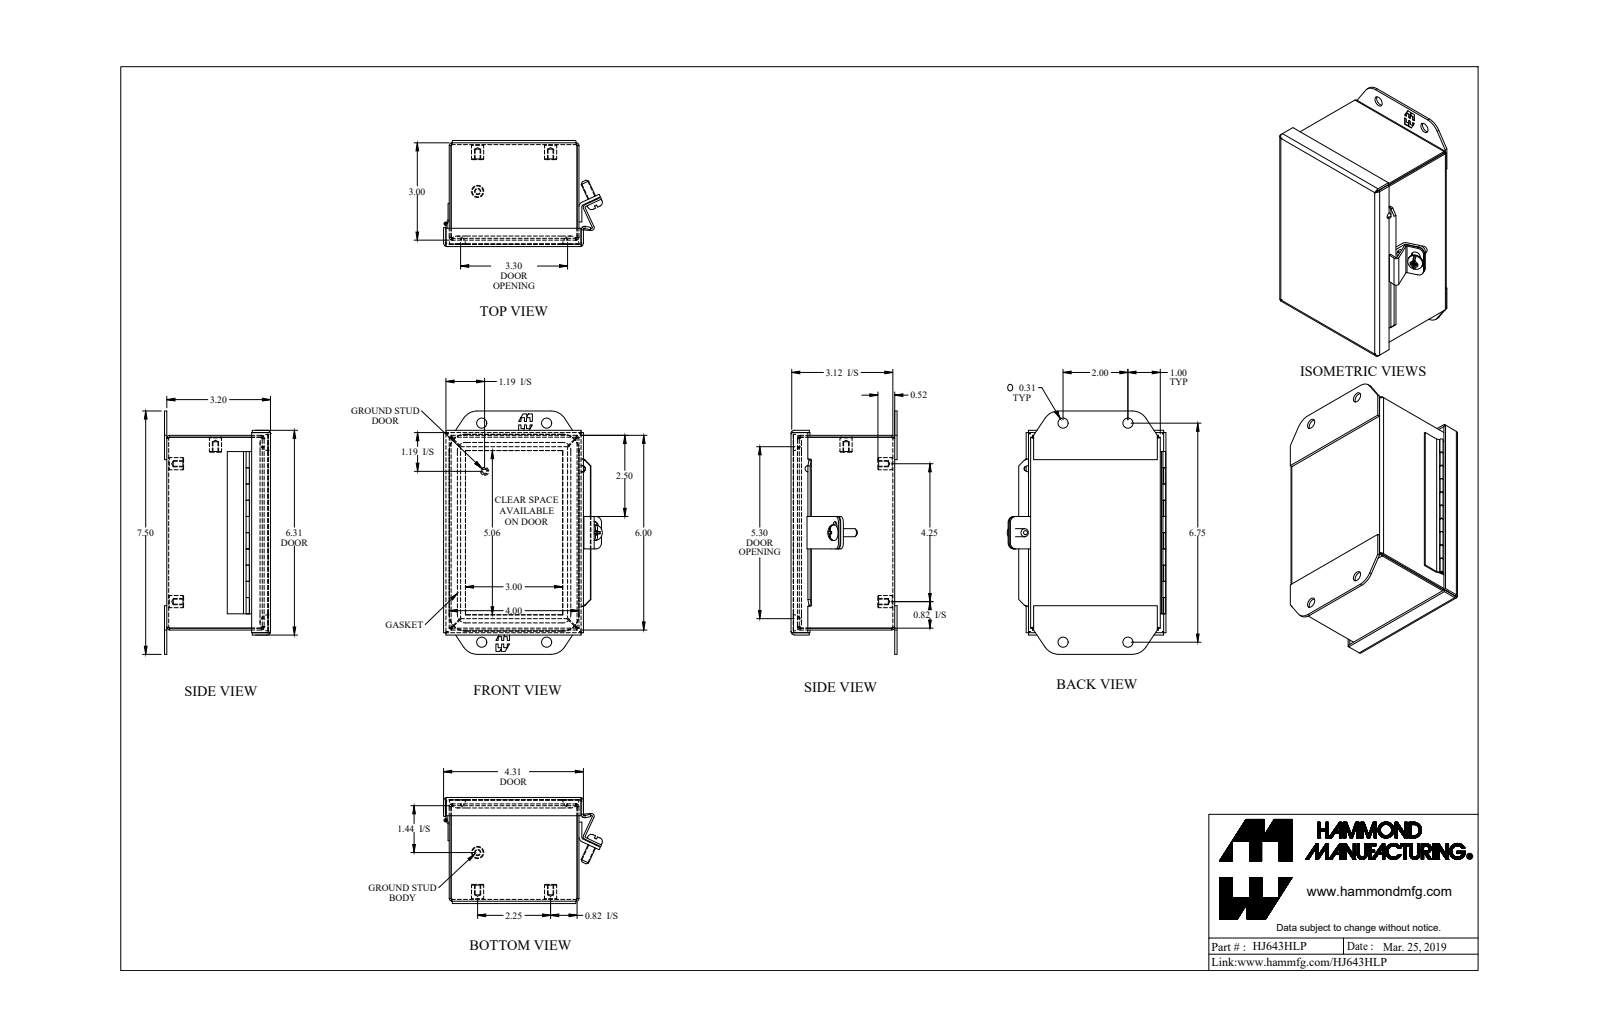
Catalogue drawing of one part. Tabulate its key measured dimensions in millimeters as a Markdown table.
| quantity | value |
| --- | --- |
| part name | HJ643HLP |
| STEP written by | SolidWorks 2018 (AUTOMOTIVE_DESIGN) |
| units | millimeters |
| bodies | 17 solids, 574 faces (307 planar, 165 cylindrical, 102 other) |
| overall size | 190.5 × 124.4 × 83 |
| volume | 177 300 mm³ |
| surface area | 221 000 mm² |
| round holes (diameter × count) | 4 × 5, 8 × 4, 1.3 × 1, 5.4 × 1 |
| round bosses / shafts (diameter × count) | 9.5 × 5, 6.4 × 2, 12.2 × 1, 4.8 × 1, 2.5 × 1, 1.1 × 1 |
| partial cylindrical surfaces (radius × count) | 4.8 × 14, 0.7 × 10, 2.2 × 10, 0.9 × 5, 2.7 × 5, 6.4 × 4, 12.7 × 4, 12.7 × 4 |
| main face-to-face distances | 1.4, 1.8, 81.2, 100.2, 79.4, 1.4, 77.9, 79.8, 151, 101.6 |
| hole center spacings | 31.9, 139.8, 62.6, 149.8, 50.8, 108, 171.5, 178.8 |
